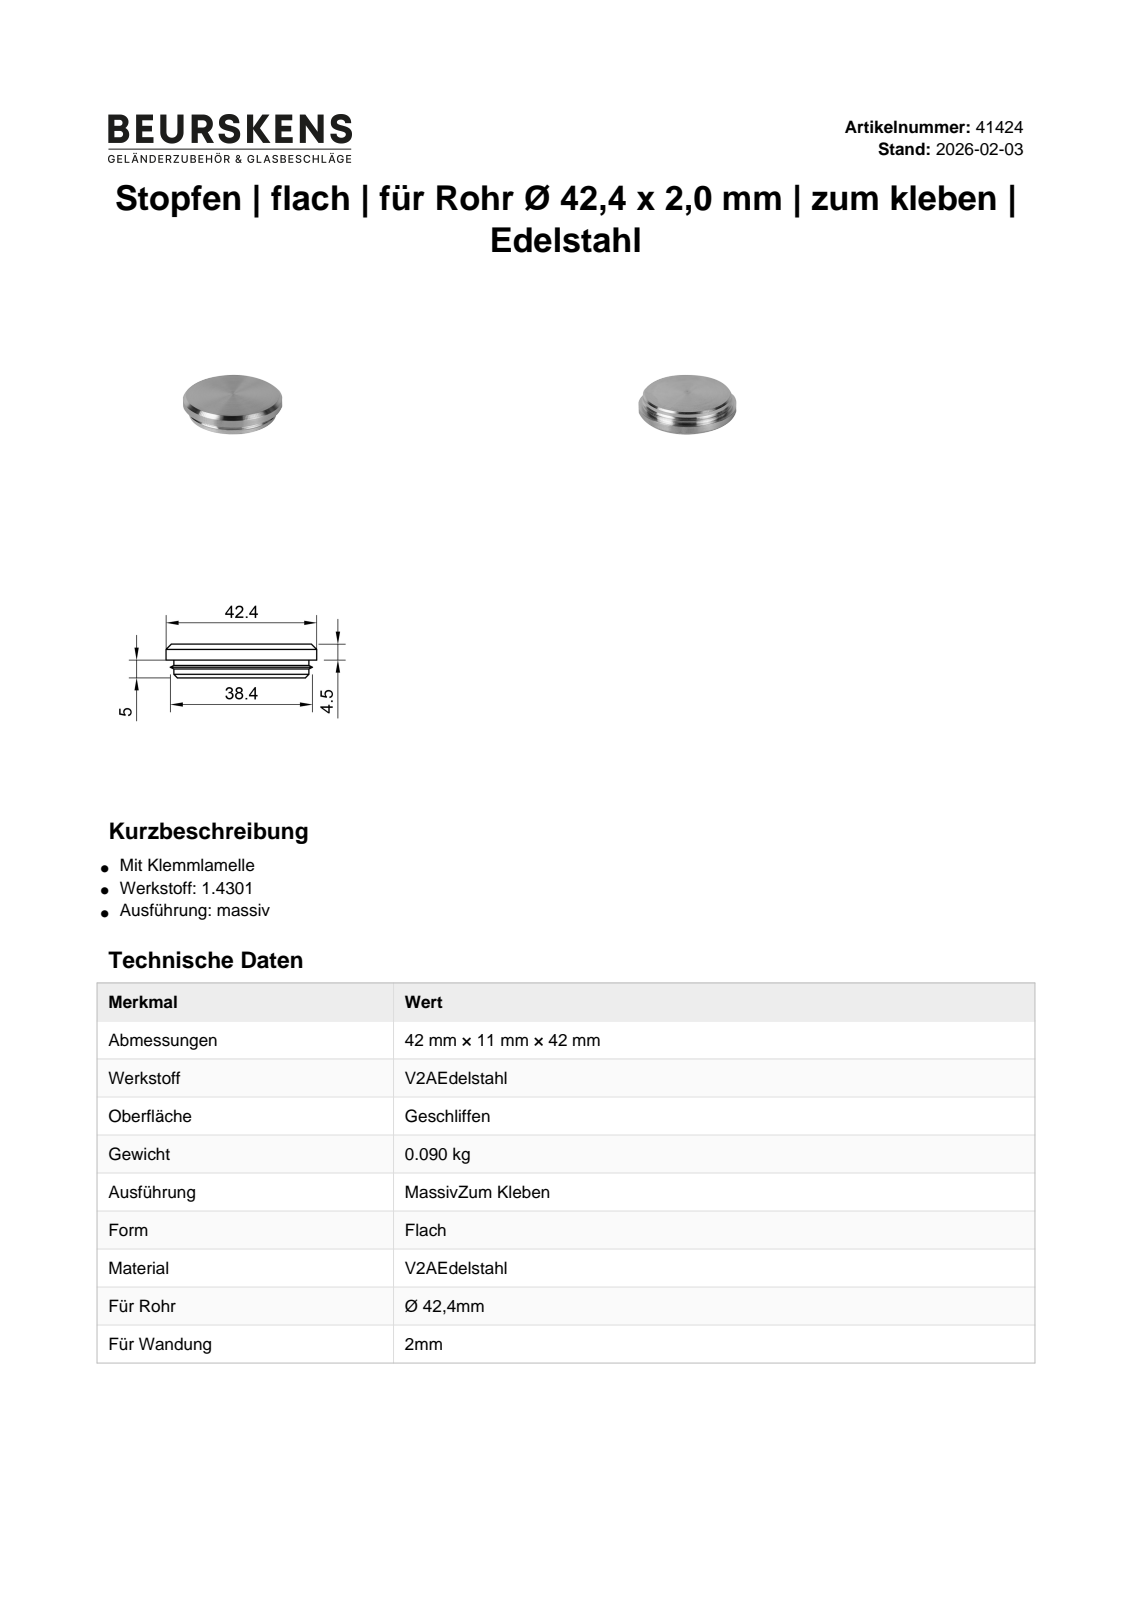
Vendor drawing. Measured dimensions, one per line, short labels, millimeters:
name: 41424
written by: Autodesk Inventor 2022 (AUTOMOTIVE_DESIGN)
unit: mm
bodies: 1 solid, 10 faces (3 planar, 3 cylindrical, 4 other)
size: 42.4 × 42.4 × 9.5
volume: 11 880 mm³; area: 3 984 mm²
bosses: 1× ⌀42.4, 1× ⌀38
face distances: 9.5, 5, 4.5
